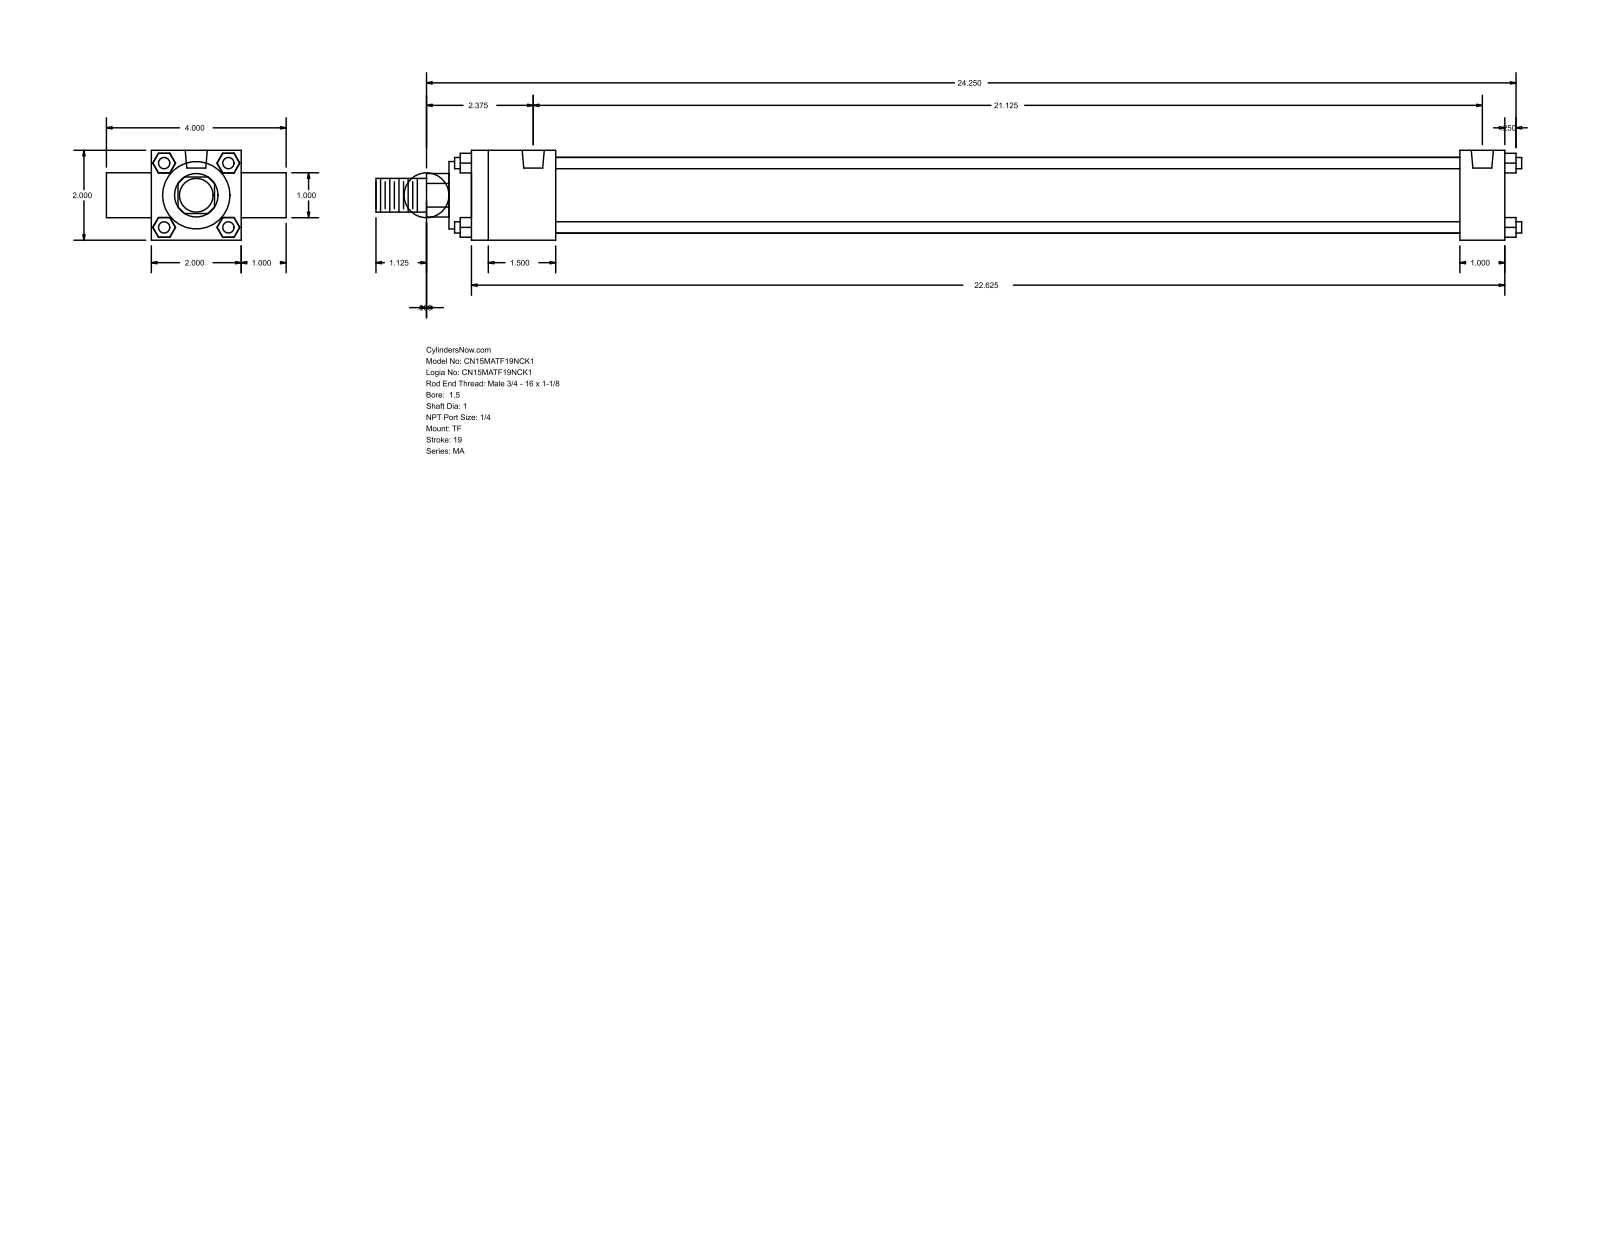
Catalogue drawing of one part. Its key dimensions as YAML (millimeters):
part_name: "MA_TF__0150_1"
step_written_by: "GSSL Pune (CONFIG_CONTROL_DESIGN)"
units: millimeters
bodies: {solids: 0, faces: 120, planar: 92, cylindrical: 28, other: 0}
overall_size: [647.7, 101.6, 50.8]
round_holes:
  - {diameter: 7.94, count: 3}
  - {diameter: 12.49, count: 2}
round_bosses_or_shafts:
  - {diameter: 6.35, count: 4}
  - {diameter: 25.4, count: 2}
  - {diameter: 42.93, count: 1}
  - {diameter: 38.1, count: 1}
  - {diameter: 19.05, count: 1}
partial_cylinders:
  - {radius: 12.29, count: 1}
face_to_face_distances: [50.8, 25.4, 584.2, 76.2, 6.35, 47.63, 558.8, 511.17, 536.57, 596.9]
hole_center_spacings: [536.57]
